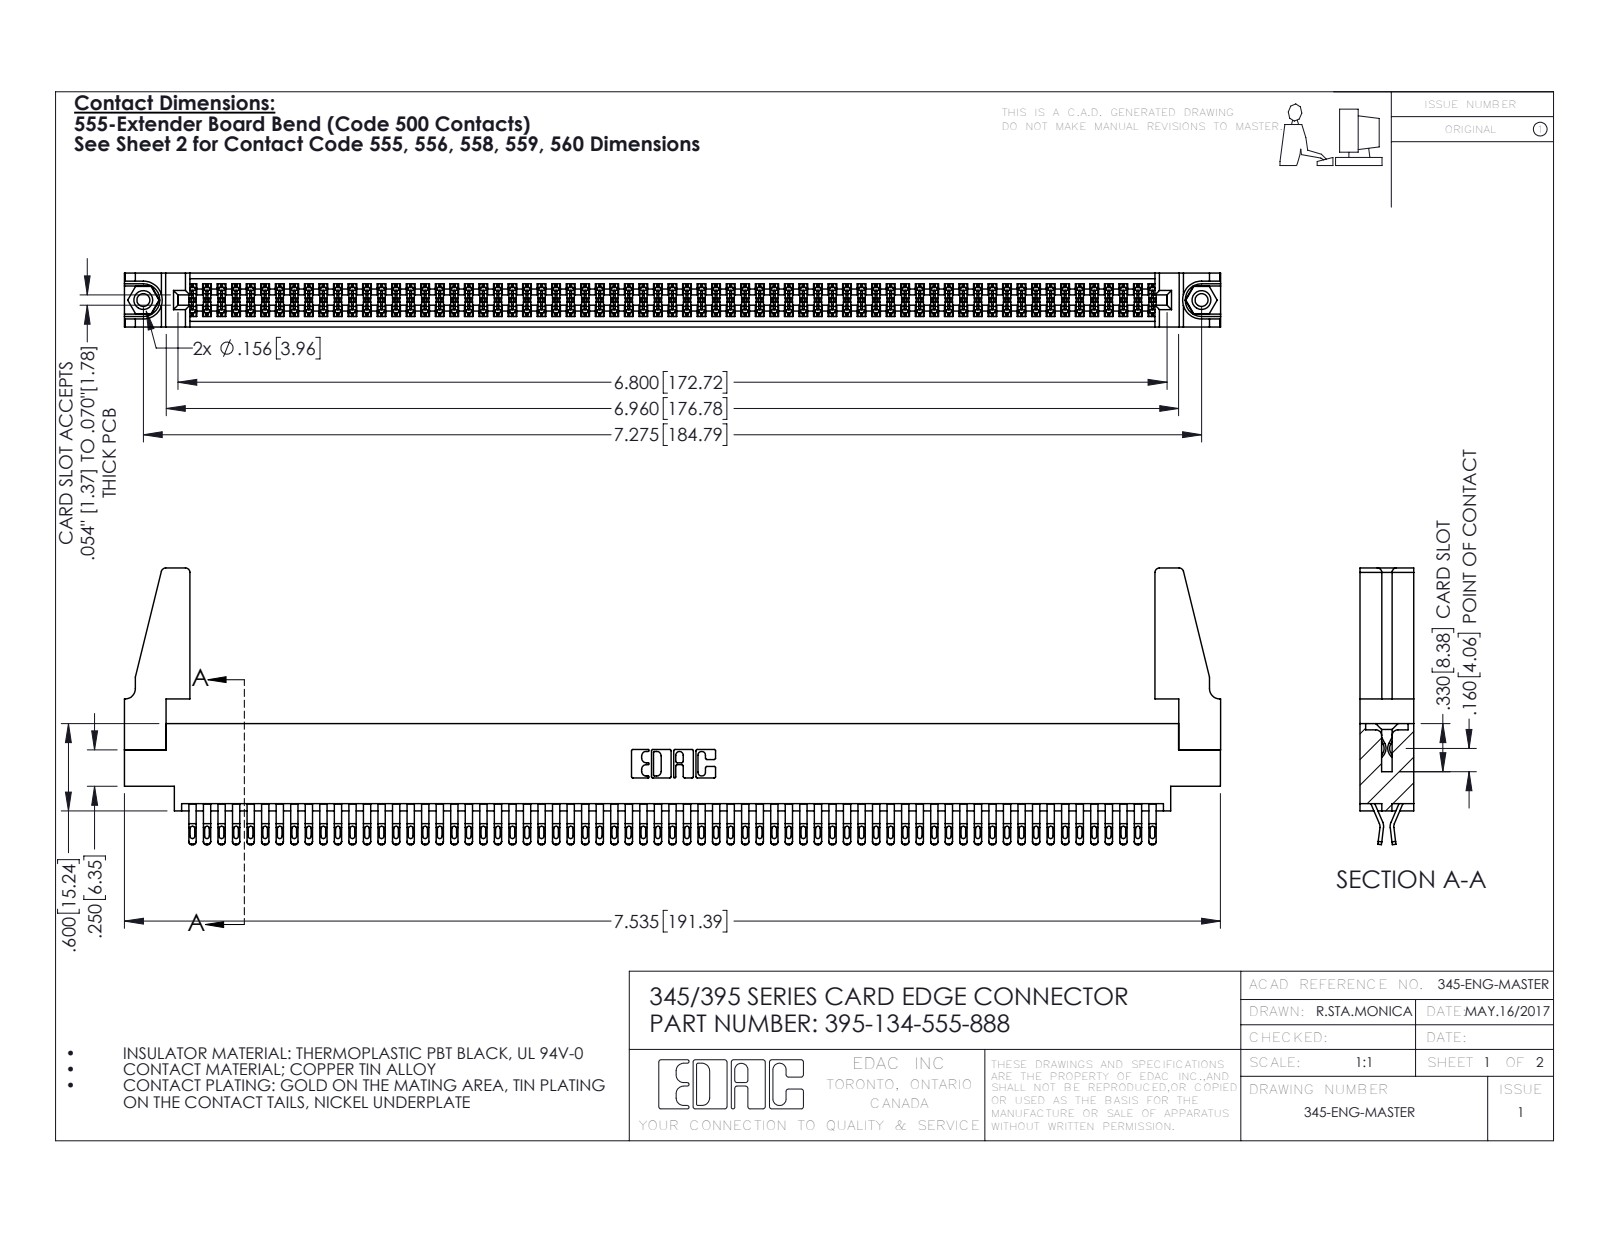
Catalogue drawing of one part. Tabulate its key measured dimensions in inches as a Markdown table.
| quantity | value |
| --- | --- |
| part name | 345-220-078_345-220-088; 395-134-555-888; 345-292-001_555 Tail; 345 Part_0.170 Offset - 0.156 Dia-TH (+1 more) |
| STEP written by | SolidWorks 2016 (CONFIG_CONTROL_DESIGN) |
| units | inches |
| bodies | 139 solids, 7758 faces (4310 planar, 3432 cylindrical, 16 other) |
| overall size | 7.536 × 1.902 × 0.37 |
| volume | 1.364 in³ |
| surface area | 51.67 in² |
| round holes (diameter × count) | 0.089 × 2, 0.125 × 2, 0.156 × 2, 0.064 × 1 |
| round bosses / shafts (diameter × count) | 0.155 × 2 |
| partial cylindrical surfaces (radius × count) | 0.016 × 335, 0.02 × 268, 0.006 × 201, 0.01 × 22, 0.03 × 8, 0.007 × 6, 0.031 × 6, 0.026 × 3 |
| main face-to-face distances | 0.072, 0.298, 0.37, 0.025, 0.098, 0.272, 0.2, 0.225, 0.175, 0.149 |
| hole center spacings | 0.27, 7.039, 7.275 |
